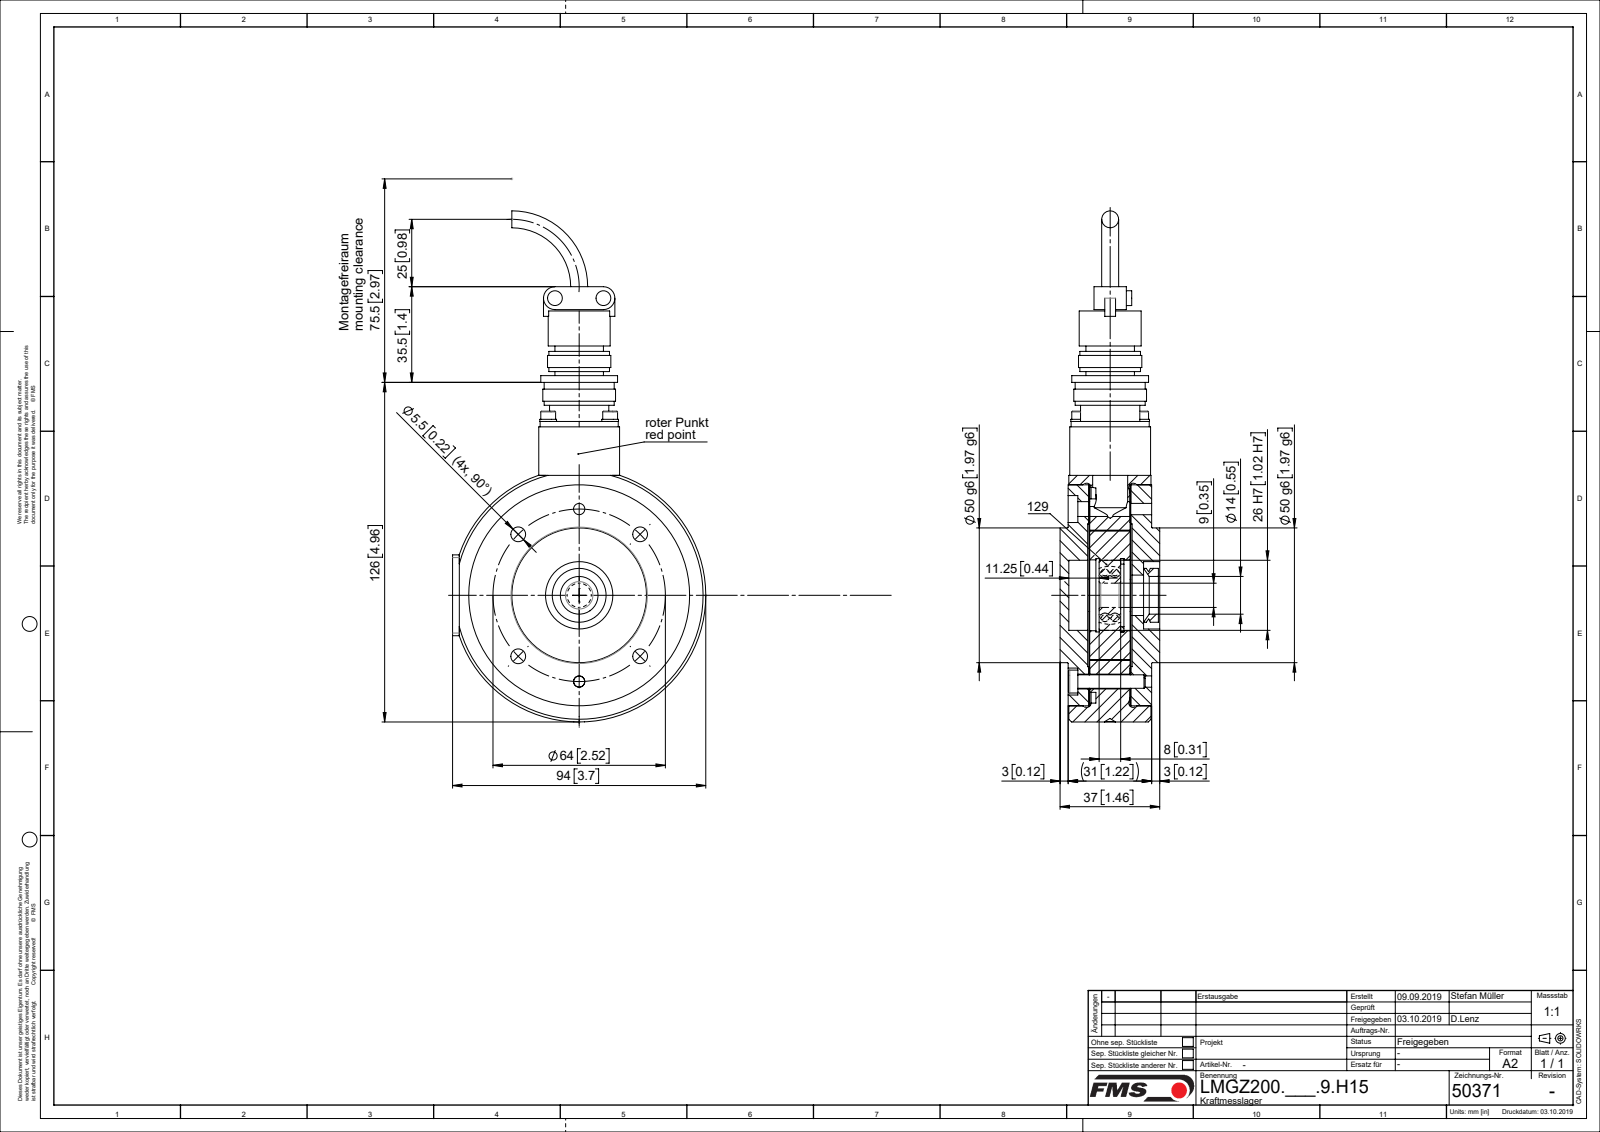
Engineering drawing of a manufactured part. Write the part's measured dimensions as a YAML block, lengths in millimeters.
part_name: "L50371_STP; L5112204; L49012; TEIL1 (+8 more)"
step_written_by: "Mechanical Desktop 2009 (CONFIG_CONTROL_DESIGN)"
units: millimeters
bodies: {solids: 24, faces: 504, planar: 150, cylindrical: 284, other: 70}
overall_size: [189.65, 94, 37]
volume: 235437
surface_area: 91883
round_holes:
  - {diameter: 2.6, count: 8}
  - {diameter: 3.4, count: 8}
  - {diameter: 5.5, count: 6}
  - {diameter: 3.2, count: 4}
  - {diameter: 4.33, count: 4}
  - {diameter: 6, count: 4}
  - {diameter: 6.6, count: 4}
  - {diameter: 10, count: 2}
  - {diameter: 13, count: 2}
  - {diameter: 9, count: 1}
  - {diameter: 14, count: 1}
  - {diameter: 15, count: 1}
round_bosses_or_shafts:
  - {diameter: 3, count: 8}
  - {diameter: 5.5, count: 6}
  - {diameter: 6.2, count: 4}
  - {diameter: 2.5, count: 4}
  - {diameter: 82, count: 1}
  - {diameter: 72, count: 1}
  - {diameter: 50, count: 1}
  - {diameter: 28.5, count: 1}
partial_cylinders:
  - {radius: 1, count: 4}
  - {radius: 4, count: 2}
  - {radius: 4.25, count: 2}
  - {radius: 8, count: 2}
  - {radius: 47, count: 1}
face_to_face_distances: [15.25, 23.25, 23, 8, 7.75, 15, 15.5, 0.5, 7.25, 11]
hole_center_spacings: [16.26, 23, 32, 24.49, 32.53, 45.26, 59.13, 62.77]
